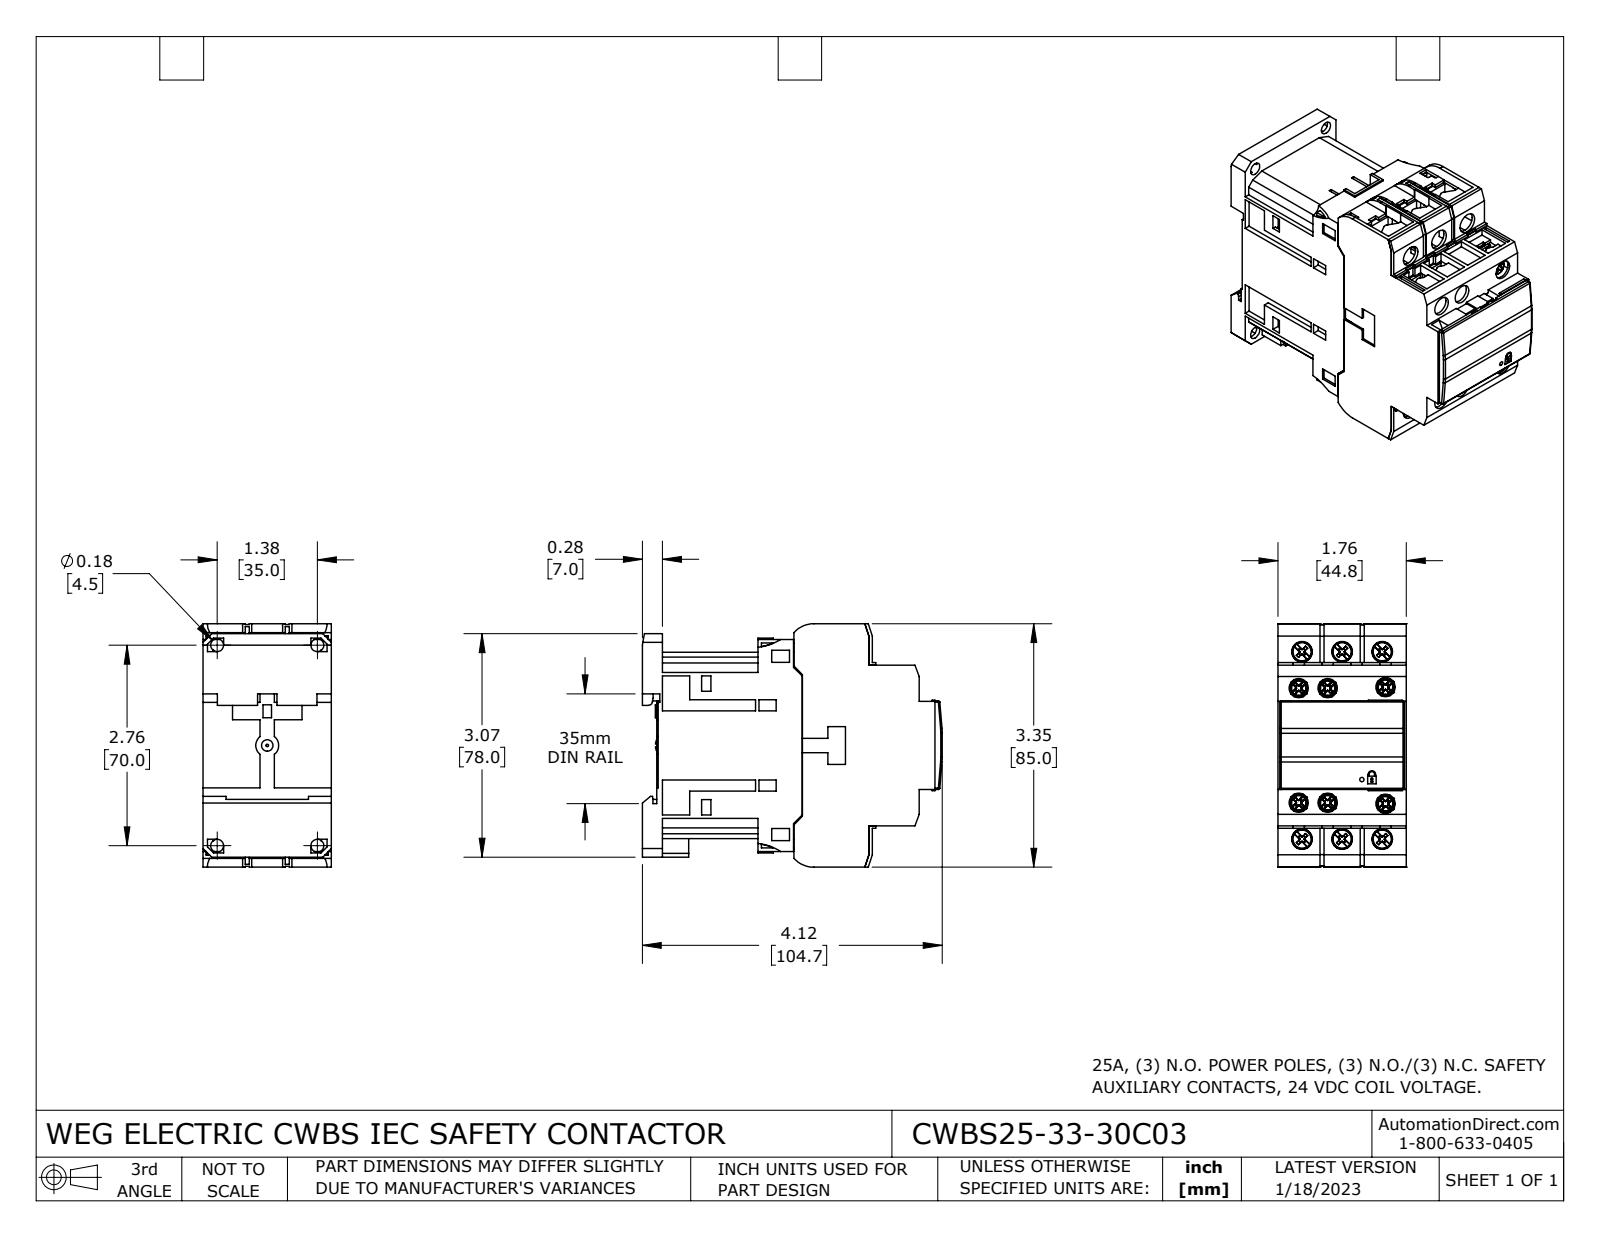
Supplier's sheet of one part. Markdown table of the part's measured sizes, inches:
| quantity | value |
| --- | --- |
| part name | CWBS25-33-30C03 |
| STEP written by | SolidWorks 2021 (CONFIG_CONTROL_DESIGN) |
| units | inches |
| bodies | 42 solids, 3062 faces (1894 planar, 647 cylindrical, 521 other) |
| overall size | 4.122 × 3.346 × 1.764 |
| volume | 16.15 in³ |
| surface area | 115.3 in² |
| round holes (diameter × count) | 0.124 × 6, 0.142 × 6, 0.264 × 6, 0.283 × 6, 0.177 × 4, 0.236 × 2, 0.059 × 1 |
| round bosses / shafts (diameter × count) | 0.201 × 6, 0.169 × 6, 0.157 × 6, 0.138 × 6, 0.107 × 6 |
| partial cylindrical surfaces (radius × count) | 0.008 × 72, 0.012 × 54, 0.004 × 48, 0.02 × 37, 0.028 × 24, 0.071 × 12, 0.081 × 12, 0.964 × 12 |
| main face-to-face distances | 1.764, 0.047, 1.823, 1.827, 0.024, 0.272, 0.646, 0.217, 3.807, 0.094 |
| hole center spacings | 0.165, 0.551, 0.664, 0.695, 0.829, 1.243, 2.272, 2.396 |
